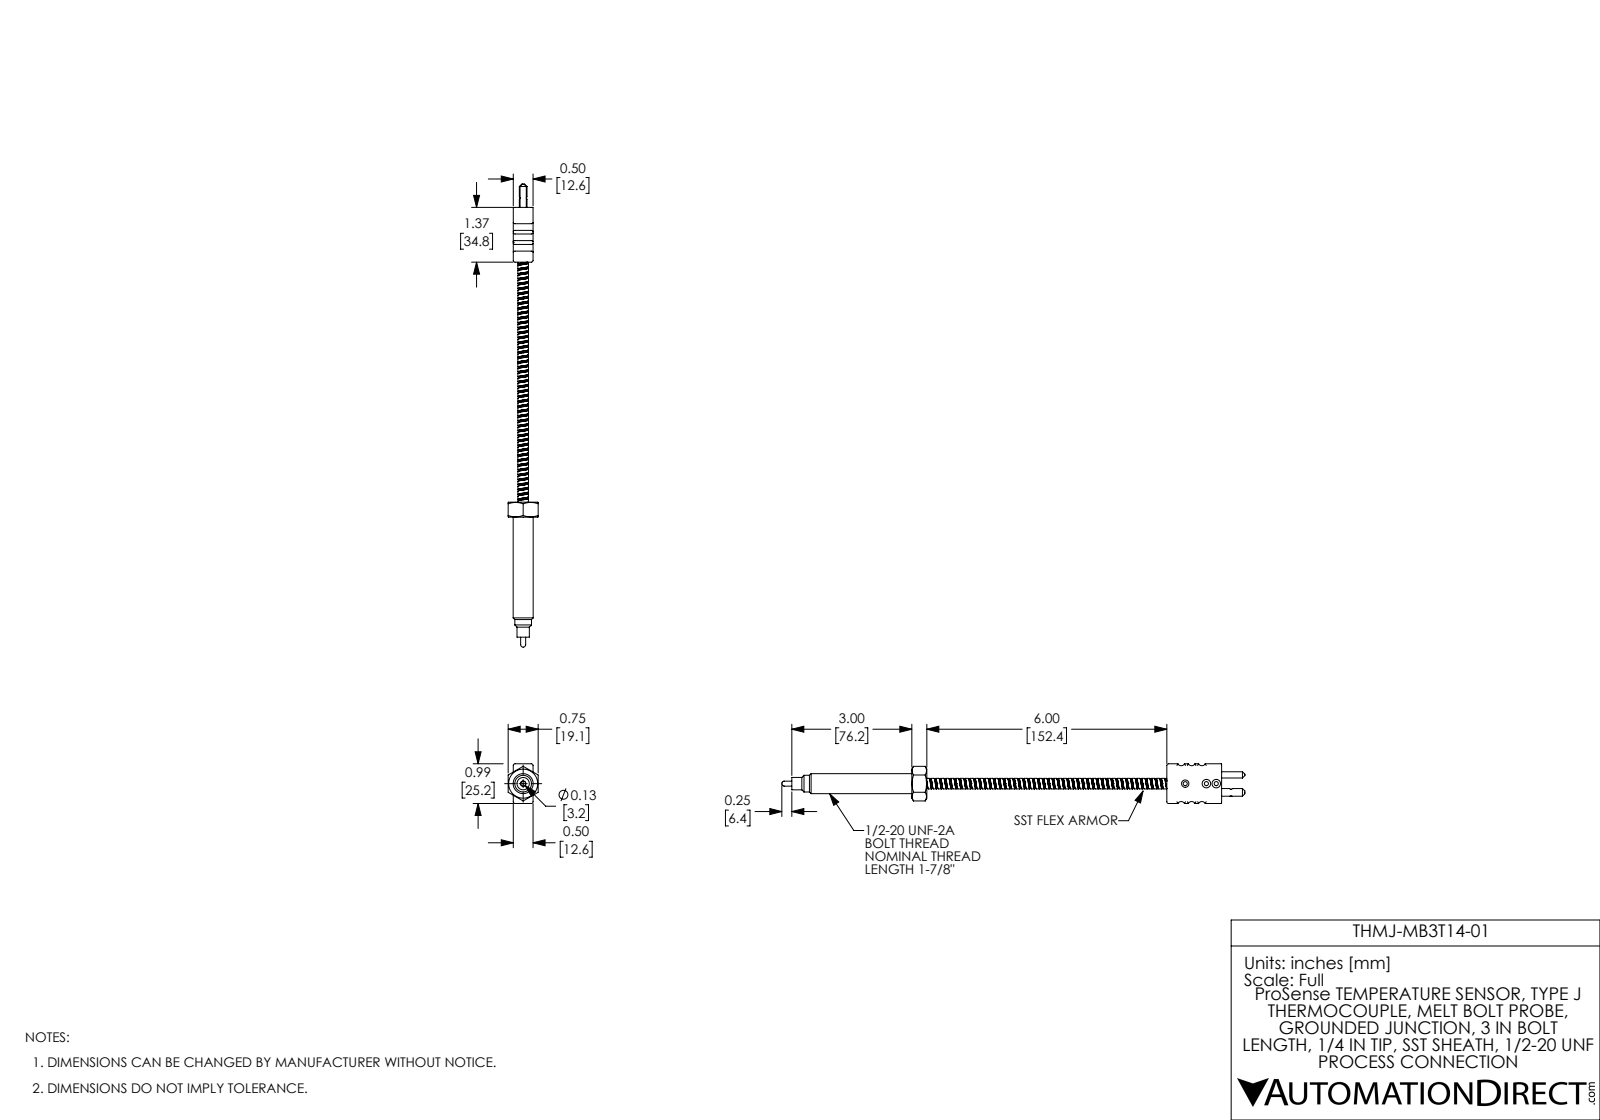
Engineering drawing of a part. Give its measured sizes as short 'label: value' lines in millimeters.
name: THMJ-MB3T14-01
written by: SolidWorks 2017 (AUTOMOTIVE_DESIGN)
unit: mm
bodies: 3 solids, 312 faces (69 planar, 172 cylindrical, 71 other)
size: 294 × 25.2 × 19.1
volume: 27 610 mm³; area: 12 390 mm²
holes: 2× ⌀2.6, 2× ⌀4, 1× ⌀3.4, 1× ⌀4.7, 1× ⌀7.5, 1× ⌀7.8
bosses: 1× ⌀12.7, 1× ⌀10.6, 1× ⌀7.8, 1× ⌀7.1, 1× ⌀6.7, 1× ⌀4.9, 1× ⌀4, 1× ⌀3.2
rounds: 8× R1.1, 6× R2.4, 4× R0.3
face distances: 12.6, 19.1, 187.2, 25.2, 3.2, 15.8, 34.8, 152.4, 196.7, 161.9
hole spacings: 5.5, 8.3, 14.5, 6.3, 11, 13.4, 19.7
